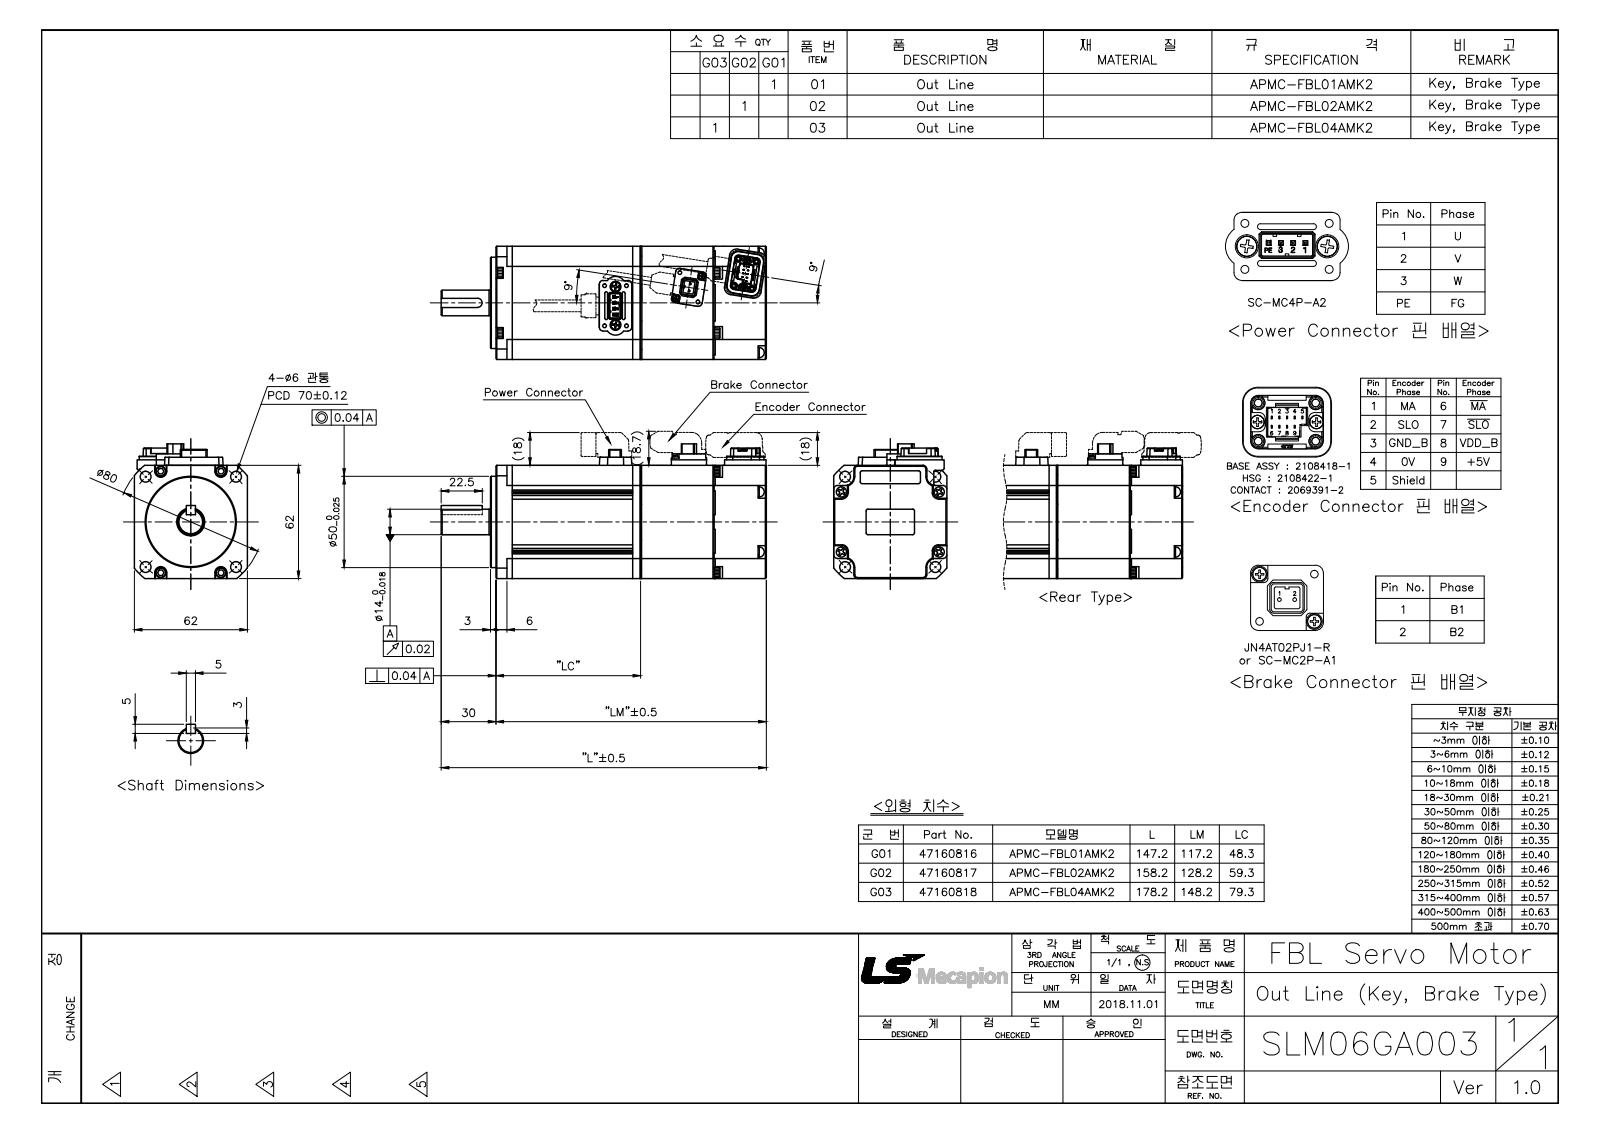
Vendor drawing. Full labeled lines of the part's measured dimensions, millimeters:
Part name (STEP PRODUCT): SLM06GA003G02_Out Line(APMC-FBL02AMK2)
STEP written by: SolidWorks 2011 (AUTOMOTIVE_DESIGN)
Units: millimetres
Bodies: 51 solids, 2086 faces (1284 planar, 582 cylindrical, 220 other)
Overall size (bounding box): 158.2 × 73.8 × 62
Volume: 448 955 mm³ · Surface area: 98 674 mm²
Round holes (diameter × count): ⌀2.1 ×10, ⌀3 ×10, ⌀3.5 ×8, ⌀2 ×6, ⌀6 ×6, ⌀3.1 ×4, ⌀1 ×2, ⌀3.3 ×1, ⌀3.4 ×1, ⌀13 ×1, ⌀15.3 ×1
Round bosses / shafts (diameter × count): ⌀5.4 ×6, ⌀5.6 ×4, ⌀5.5 ×4, ⌀4.2 ×2, ⌀3.6 ×2, ⌀3.5 ×2, ⌀2.2 ×2, ⌀0.9 ×2
Partial cylindrical surfaces — rounded edges, fillets, slot ends (radius × count): R0.2 ×20, R0.3 ×20, R1 ×14, R2 ×12, R0.15 ×9, R3 ×8, R0.45 ×7, R0.11 ×6
Main face-to-face distances: 62, 4.3, 0.5, 0.7, 46, 50.3, 44.5, 40.2, 90.5, 40.9
Hole centre spacings: 6.02, 8.5, 8.8, 9.43, 15.29, 16.01, 22.32, 31.47
